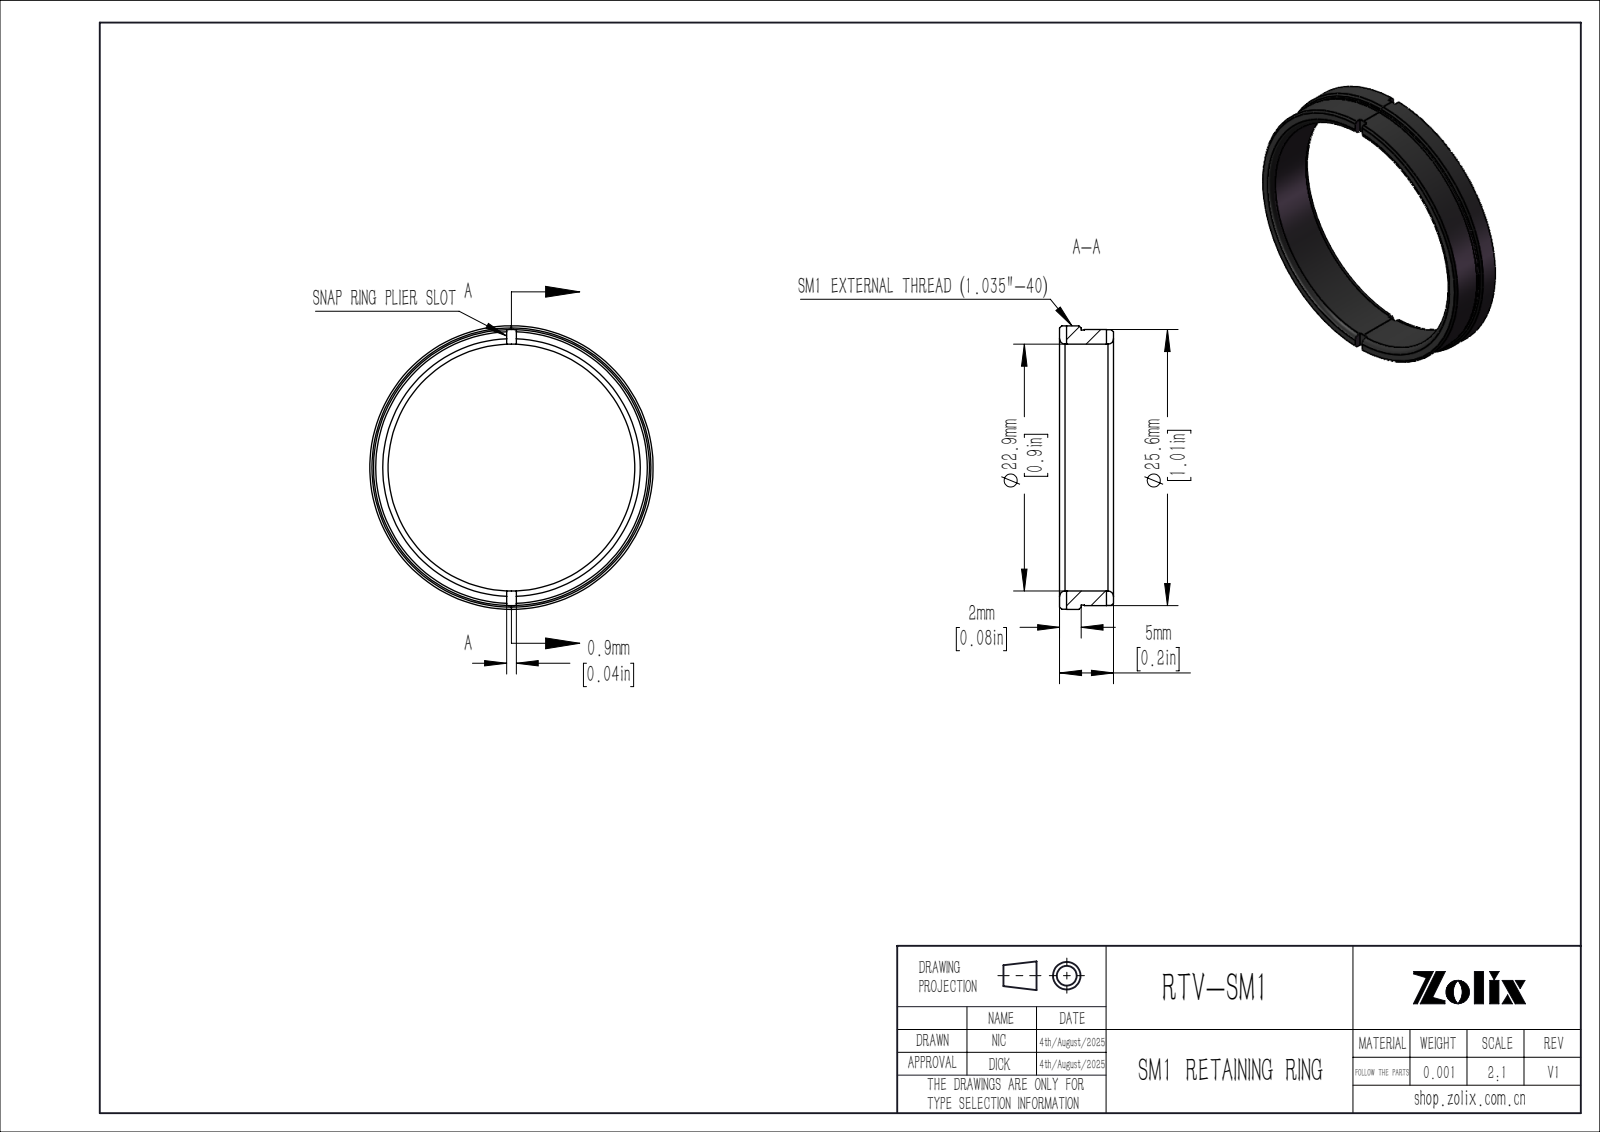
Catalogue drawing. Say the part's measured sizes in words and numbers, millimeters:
The part is named "RTV-SM1". Its 3-D file was written by "SolidWorks 2020 (CONFIG_CONTROL_DESIGN)". It is 1 solid with 36 faces: 18 planar, 8 cylindrical and 10 other. Overall it measures 26.3 by 26.3 by 5 millimeters. Its volume is 554 cubic millimeters and its surface area 981 square millimeters. Round holes: 1 of diameter 22.9. Round bosses or shafts: 1 of diameter 26.3, 1 of diameter 25.6, 1 of diameter 25.5. The main face-to-face distances are 5, 2, 3, 0.65, 4.35, 2.3, 2.7, 0.9, 1.35, 1.65.
